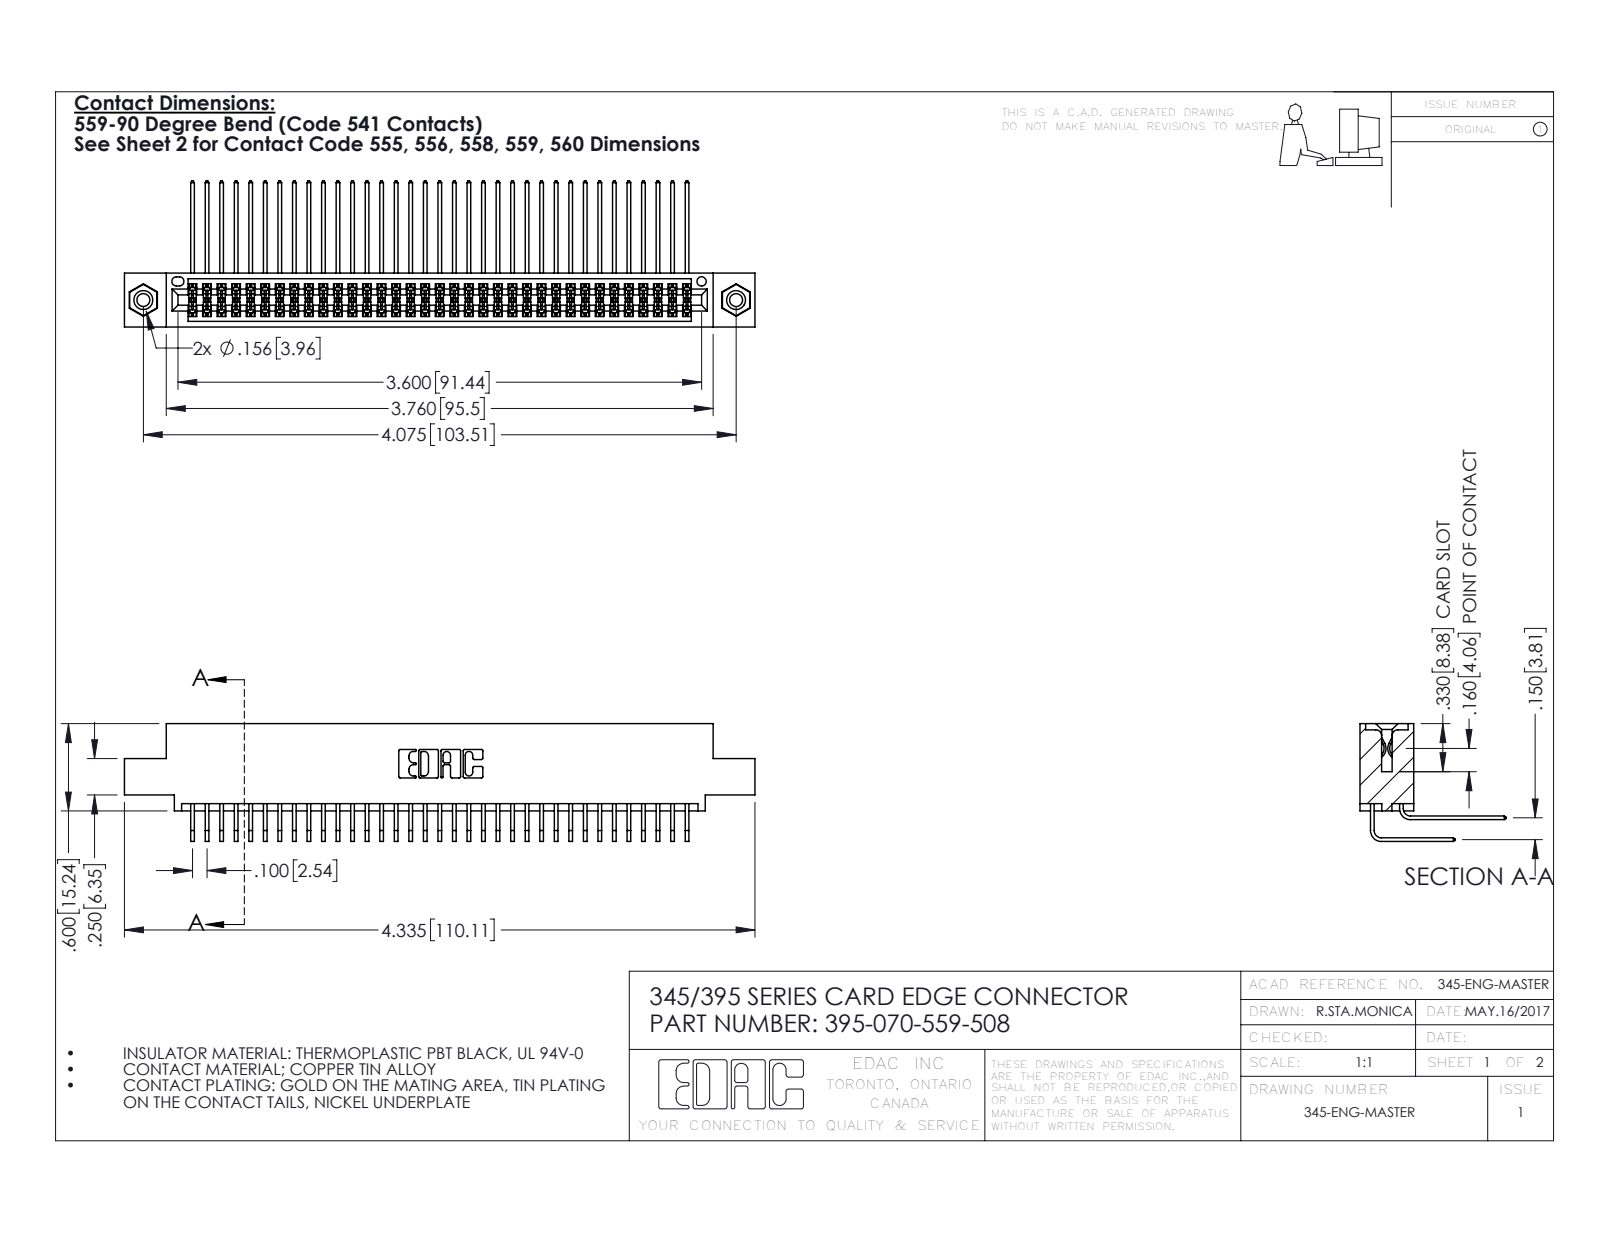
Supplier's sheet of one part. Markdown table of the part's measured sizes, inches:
| quantity | value |
| --- | --- |
| part name | 345 Part_0.110 Offset - 0.156 Dia-TI; 345-292-001_559 Tail - 2; 345-250-001_345-250-003-102; 395-070-559-508 (+1 more) |
| STEP written by | SolidWorks 2016 (CONFIG_CONTROL_DESIGN) |
| units | inches |
| bodies | 73 solids, 3830 faces (2566 planar, 1248 cylindrical, 16 other) |
| overall size | 4.335 × 1.005 × 0.809 |
| volume | 0.669 in³ |
| surface area | 28 in² |
| round holes (diameter × count) | 0.089 × 2, 0.125 × 2, 0.156 × 2, 0.064 × 1 |
| round bosses / shafts (diameter × count) | 0.155 × 2 |
| partial cylindrical surfaces (radius × count) | 0.006 × 105, 0.01 × 22, 0.007 × 6, 0.031 × 6, 0.026 × 3, 0.014 × 2, 0.019 × 2, 0.022 × 2 |
| main face-to-face distances | 0.072, 0.298, 0.37, 0.2, 0.098, 0.272, 0.025, 0.225, 0.175, 0.15 |
| hole center spacings | 0.27, 3.839, 4.075 |
